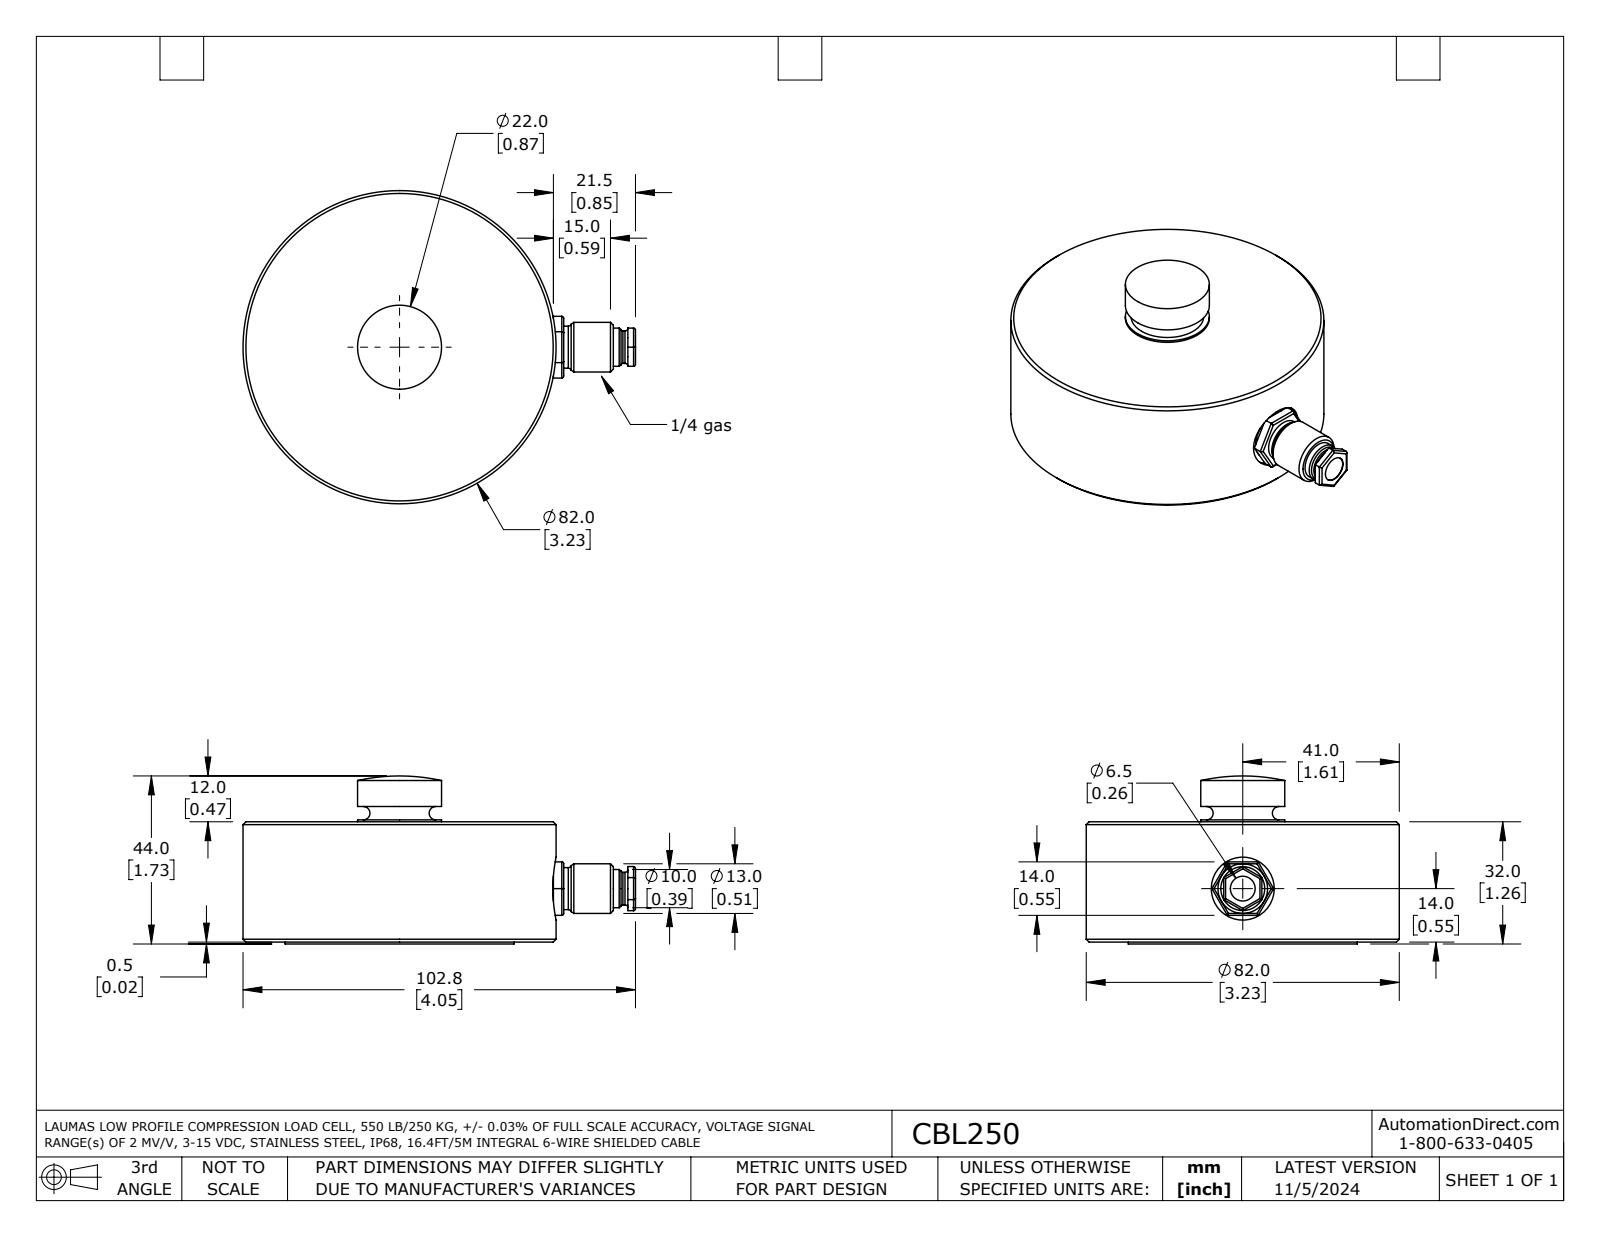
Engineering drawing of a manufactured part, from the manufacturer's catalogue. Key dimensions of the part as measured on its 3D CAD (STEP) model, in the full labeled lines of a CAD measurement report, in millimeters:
Part name (STEP PRODUCT): CBL250
STEP written by: SolidWorks 2021 (AUTOMOTIVE_DESIGN)
Units: millimetres
Bodies: 2 solids, 86 faces (31 planar, 36 cylindrical, 19 other)
Overall size (bounding box): 102.8 × 82 × 44
Volume: 170 800 mm³ · Surface area: 21 060 mm²
Round holes (diameter × count): ⌀6.5 ×1, ⌀16.5 ×1, ⌀54.6 ×1
Round bosses / shafts (diameter × count): ⌀82 ×1, ⌀60 ×1, ⌀22 ×1, ⌀13.5 ×1, ⌀13 ×1, ⌀11 ×1, ⌀10 ×1, ⌀8.5 ×1
Partial cylindrical surfaces — rounded edges, fillets, slot ends (radius × count): R0.5 ×12
Main face-to-face distances: 30.8, 0.8, 31.5, 0.5, 32, 1.2, 3.5, 32.5, 31.2, 36
